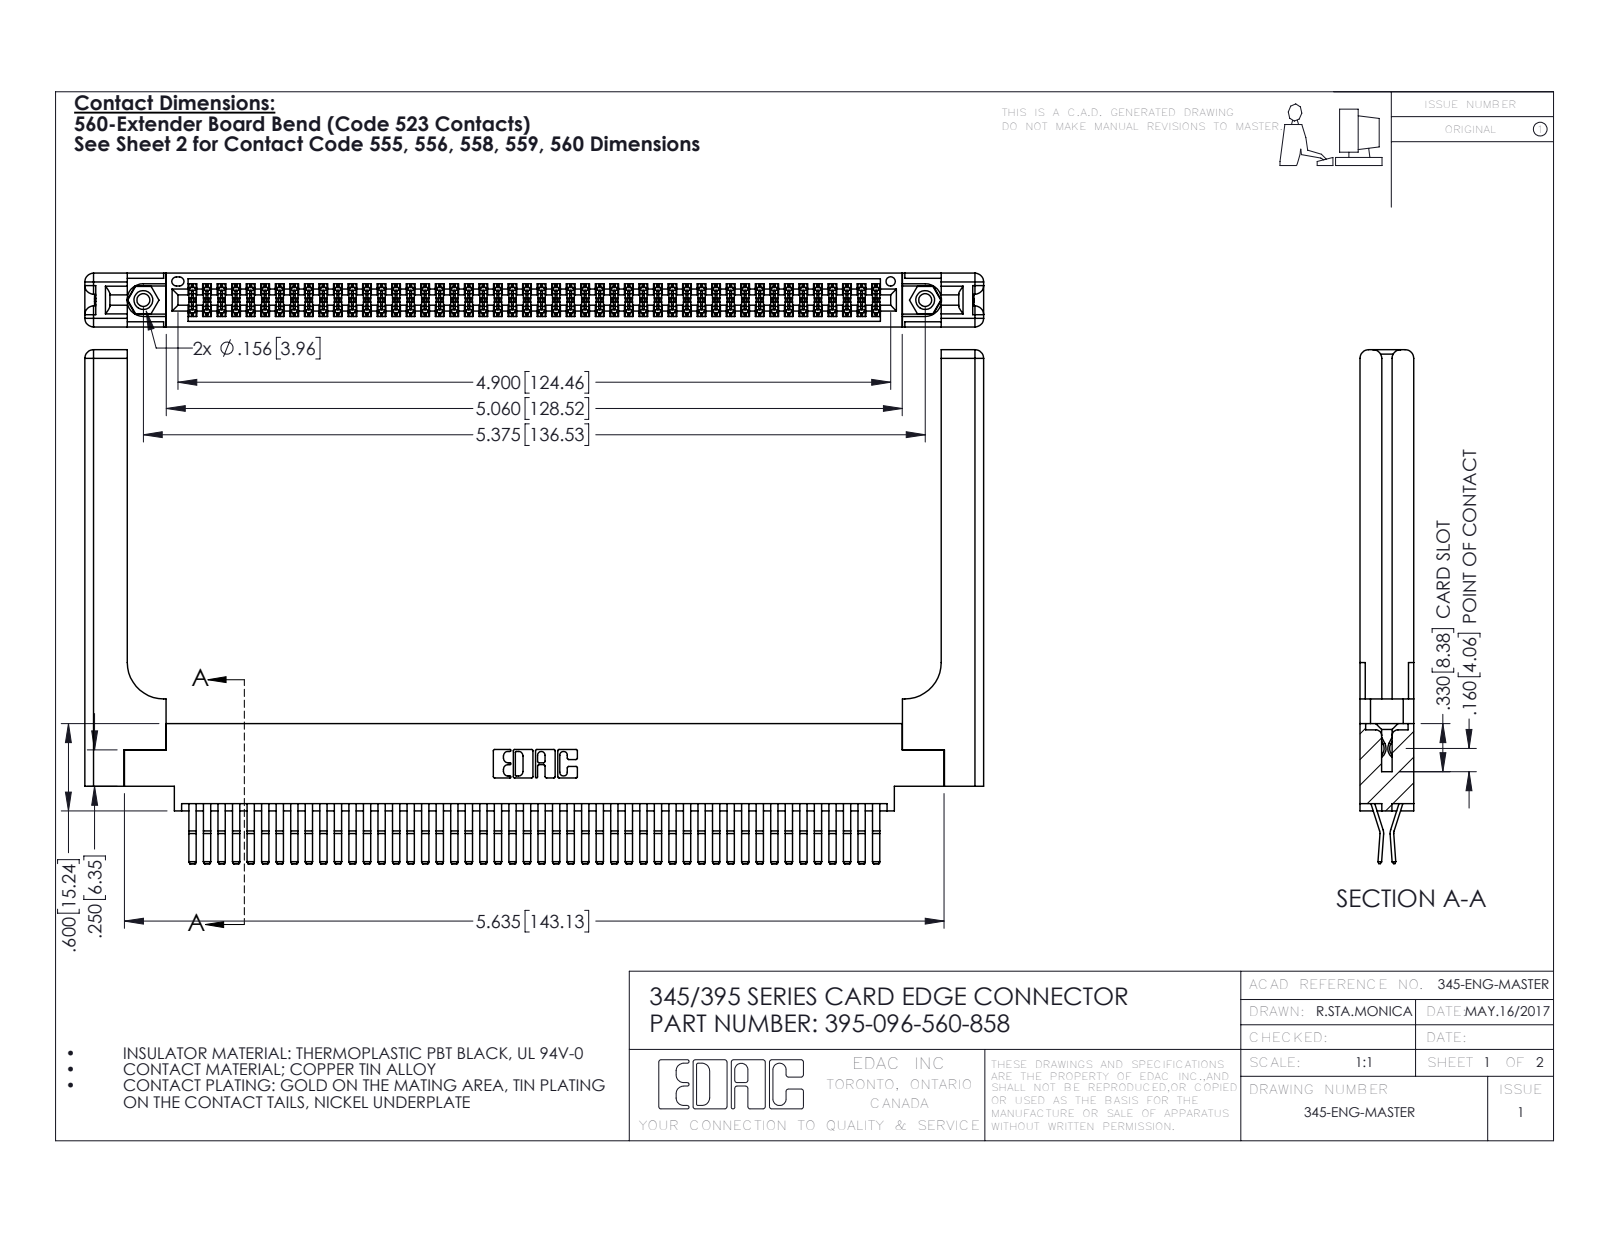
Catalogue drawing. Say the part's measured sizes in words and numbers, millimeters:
The part is named "345-220-058_345-220-058; 395-096-560-858; 345-250-001_345-250-001-102; 345 Part_0.170 Offset - 0.156 Dia-TH (+1 more)". Its 3-D file was written by "SolidWorks 2016 (CONFIG_CONTROL_DESIGN)". It is 101 solids with 5378 faces: 3400 planar, 1918 cylindrical and 60 other. Overall it measures 156.9 by 89.7 by 9.4 millimeters. Its volume is 24 290 cubic millimeters and its surface area 30 320 square millimeters. Round holes: 2 of diameter 2.3, 2 of diameter 3.2, 2 of diameter 4, 1 of diameter 1.6. Round bosses or shafts: 2 of diameter 3.9. Partial cylindrical surfaces (rounded edges, fillets, slot ends): 145 of radius 0.2, 22 of radius 0.3, 16 of radius 1.5, 6 of radius 0.2, 6 of radius 0.8, 3 of radius 0.7, 2 of radius 0.3, 2 of radius 0.4. The main face-to-face distances are 1.8, 9.4, 7.6, 0.6, 2.5, 6.9, 5.1, 5.7, 3.8, 3.8. The hole center spacings are 6.9, 130.5, 136.5.
